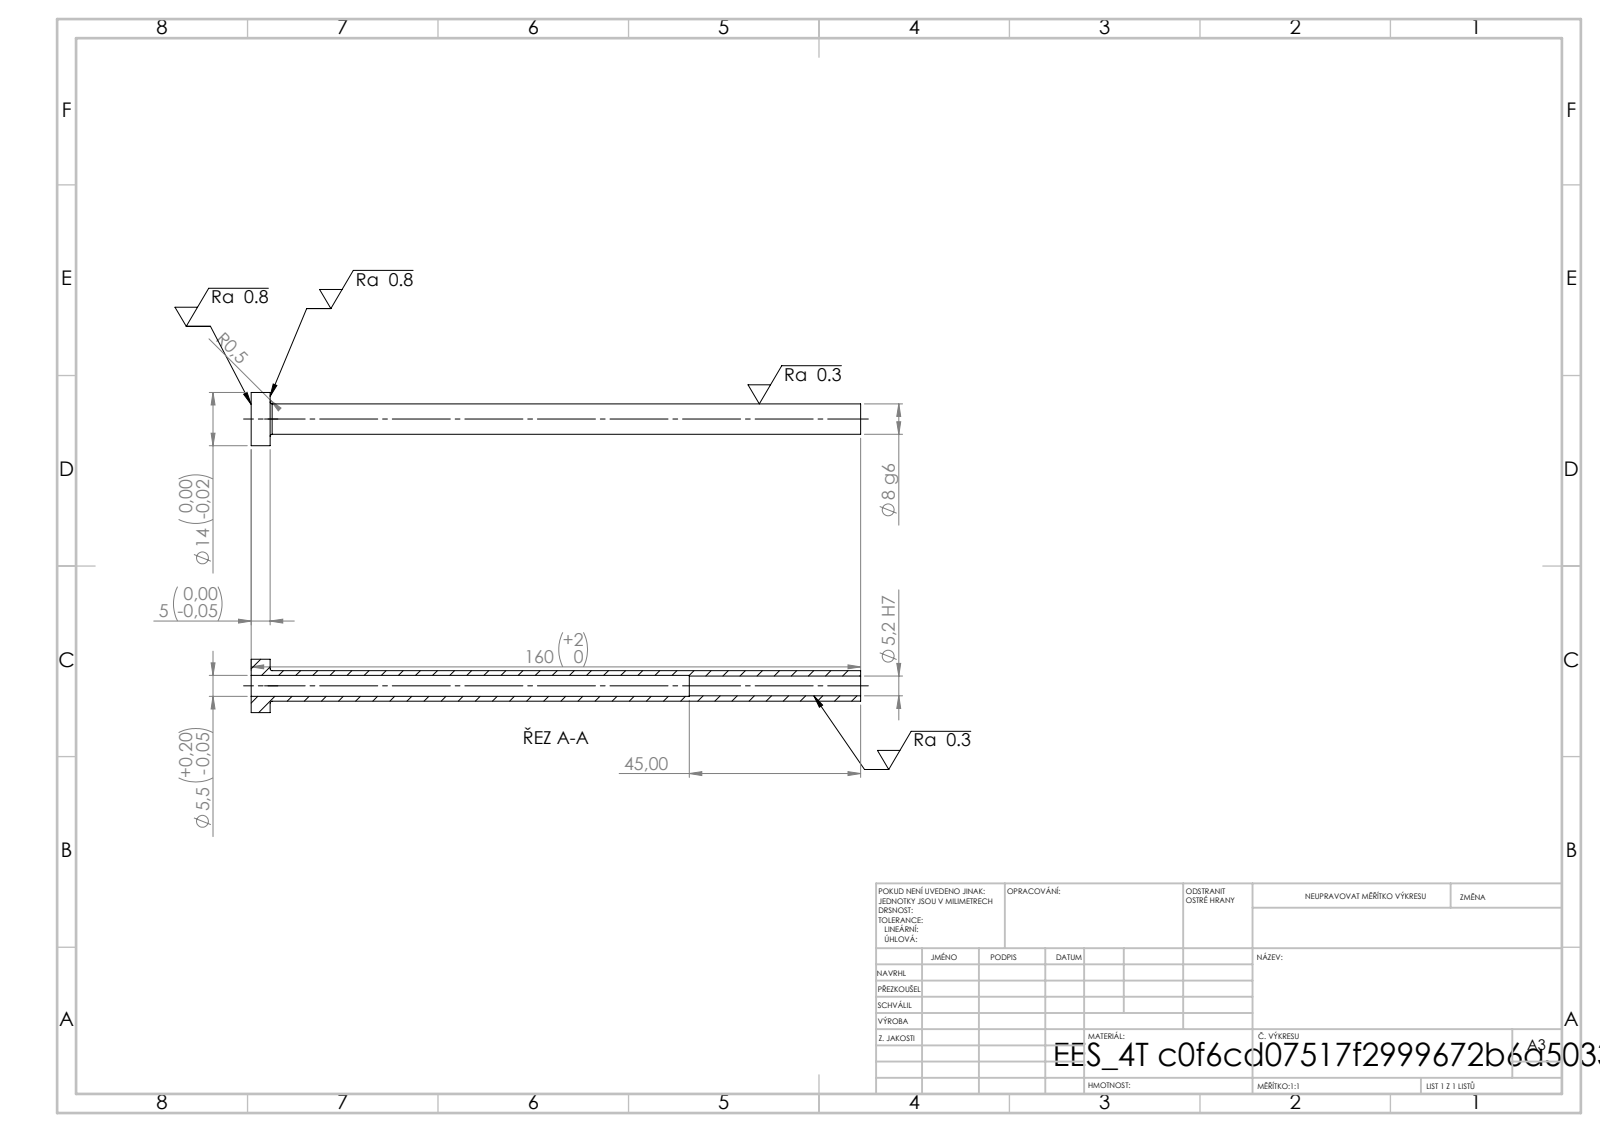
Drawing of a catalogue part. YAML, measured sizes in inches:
step_written_by: "SolidWorks 2019 (CONFIG_CONTROL_DESIGN)"
units: inches
bodies: {solids: 1, faces: 14, planar: 4, cylindrical: 8, other: 2}
overall_size: [6.299, 0.551, 0.551]
volume: 0.297
surface_area: 11
round_holes:
  - {diameter: 0.205, count: 1}
  - {diameter: 0.217, count: 1}
round_bosses_or_shafts:
  - {diameter: 0.551, count: 1}
  - {diameter: 0.315, count: 1}
face_to_face_distances: [0.197, 6.299, 6.102, 4.528, 4.331, 1.772]
